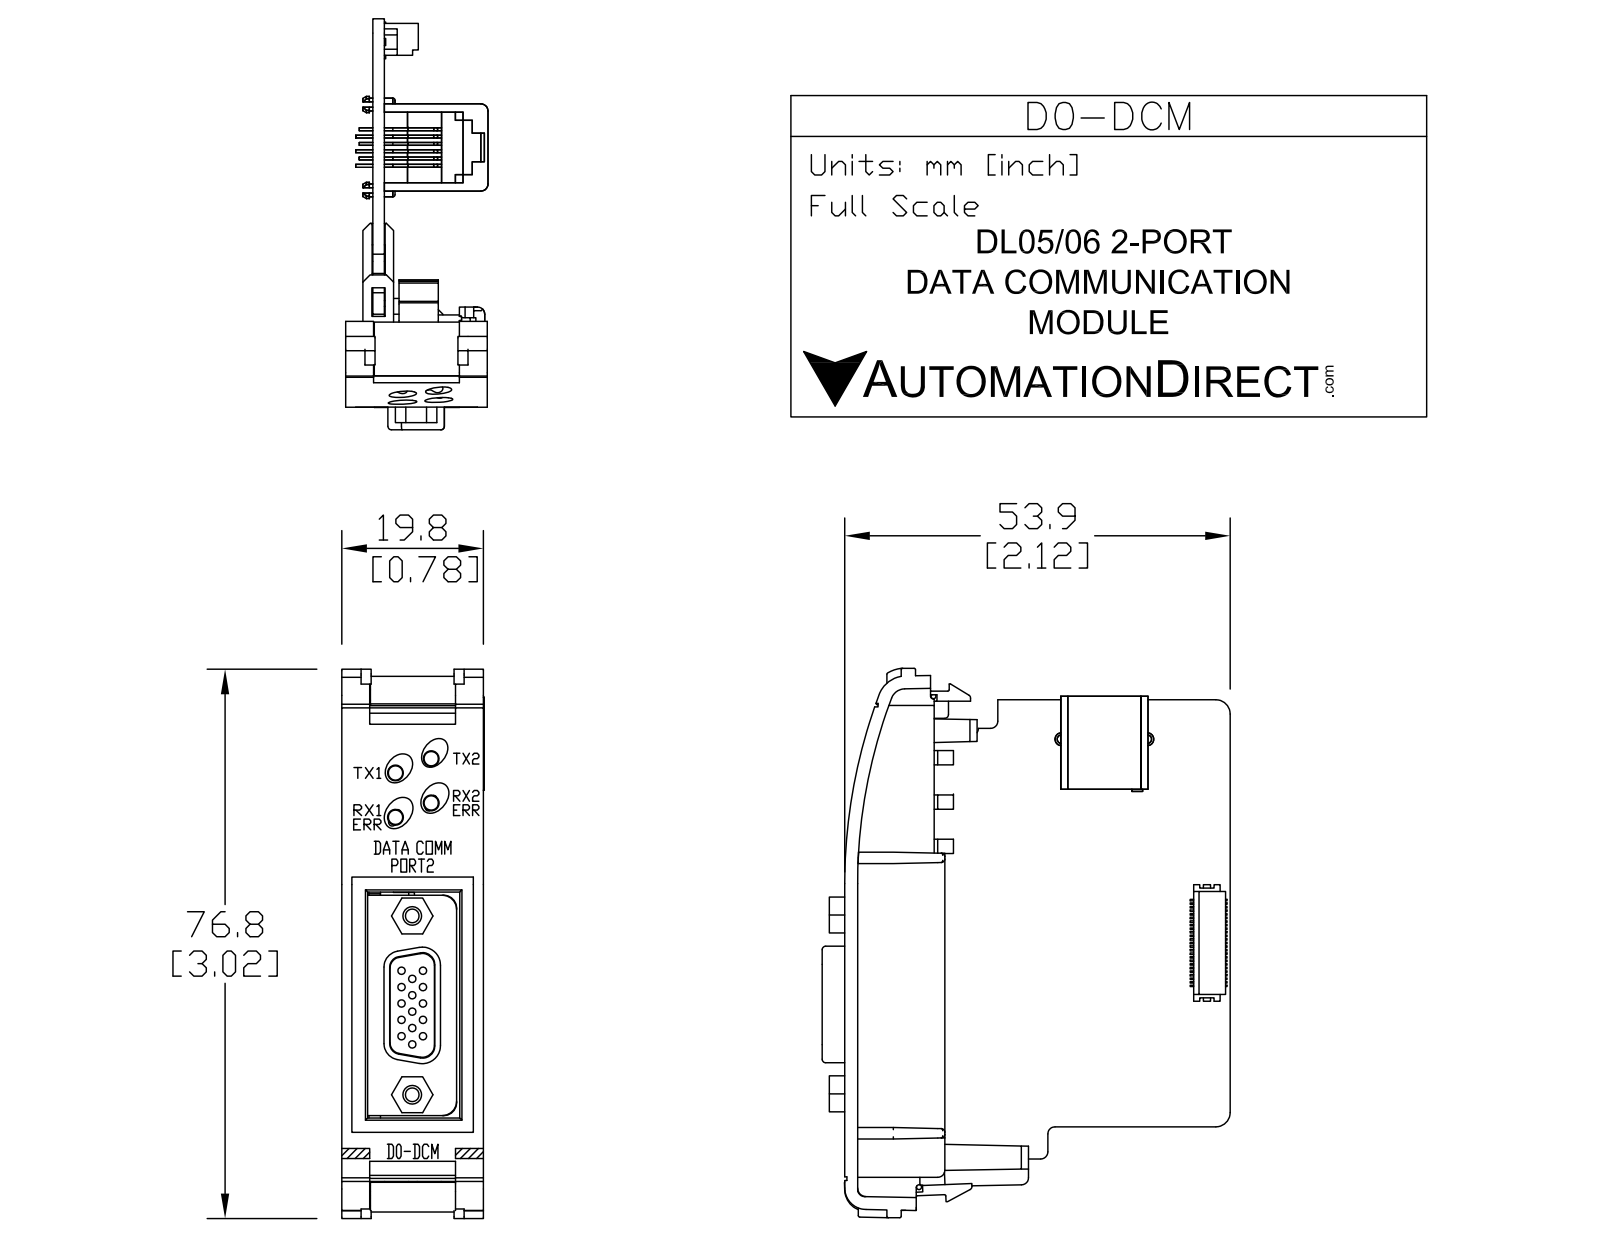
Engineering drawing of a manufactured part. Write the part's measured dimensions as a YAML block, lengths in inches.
part_name: "D0-DCM"
step_written_by: "SolidWorks 2009 (AUTOMOTIVE_DESIGN)"
units: inches
bodies: {solids: 1, faces: 327, planar: 205, cylindrical: 82, other: 40}
overall_size: [3.08, 2.399, 0.826]
volume: 0.678
surface_area: 22.1
round_holes:
  - {diameter: 0.05, count: 9}
  - {diameter: 0.1, count: 2}
round_bosses_or_shafts:
  - {diameter: 0.089, count: 4}
  - {diameter: 0.2, count: 2}
partial_cylinders:
  - {radius: 0.005, count: 4}
  - {radius: 0.03, count: 4}
  - {radius: 0.12, count: 4}
  - {radius: 0.02, count: 3}
  - {radius: 0.035, count: 3}
  - {radius: 0.025, count: 2}
  - {radius: 0.01, count: 1}
  - {radius: 0.065, count: 1}
face_to_face_distances: [0.063, 0.05, 0.631, 0.113, 0.681, 0.569, 0.581, 0.519, 0.075, 0.15]
hole_center_spacings: [0.117, 0.1, 0.183, 0.2, 0.271, 0.3, 0.365, 0.393]
